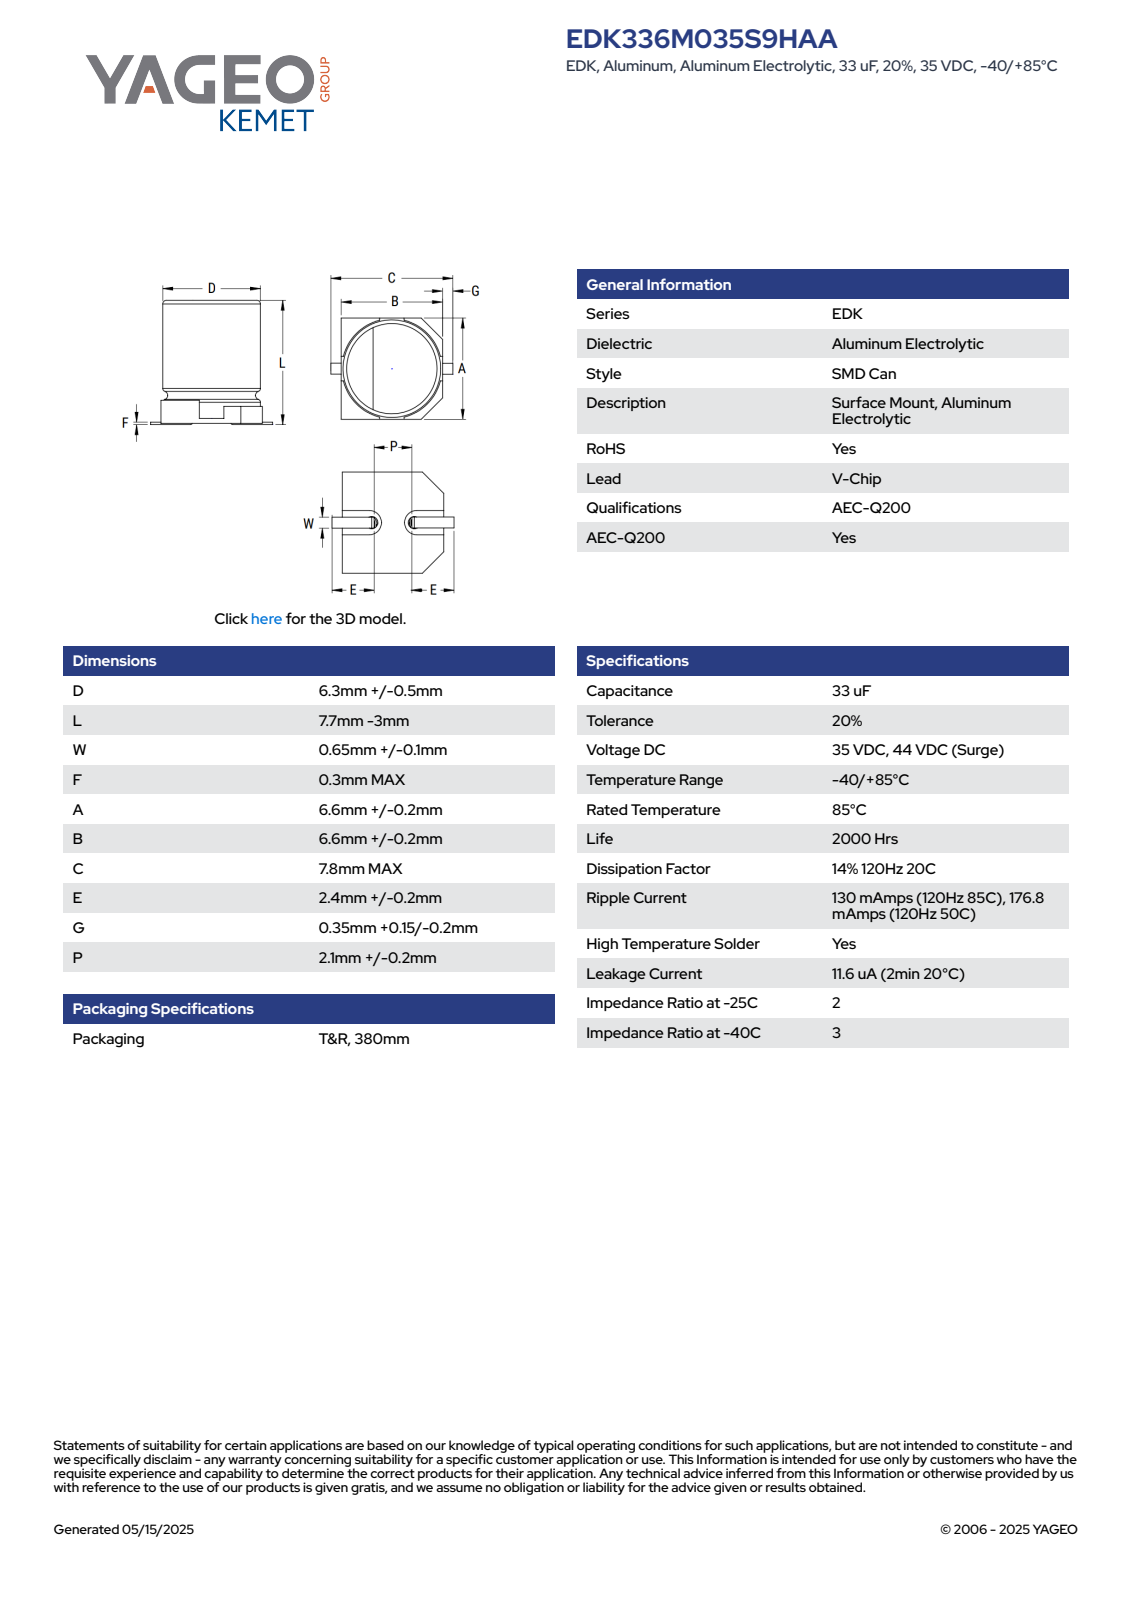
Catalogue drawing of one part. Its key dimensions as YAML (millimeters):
part_name: "CAC_S_6.3X5.4_D6.8L8W0.75F0.3A6.8B6.8C7.8E2.8P2"
step_written_by: "SolidWorks 2014 (AUTOMOTIVE_DESIGN)"
units: millimeters
bodies: {solids: 5, faces: 78, planar: 61, cylindrical: 11, other: 6}
overall_size: [8.01, 7.6, 6.8]
volume: 266
surface_area: 359
round_bosses_or_shafts:
  - {diameter: 6.5, count: 1}
partial_cylinders:
  - {radius: 0.2, count: 2}
  - {radius: 2.7, count: 1}
  - {radius: 3.4, count: 1}
face_to_face_distances: [0.4, 7.7, 7.3, 7.71, 7.31, 6.8, 2, 1.6, 5.7, 5.71]
